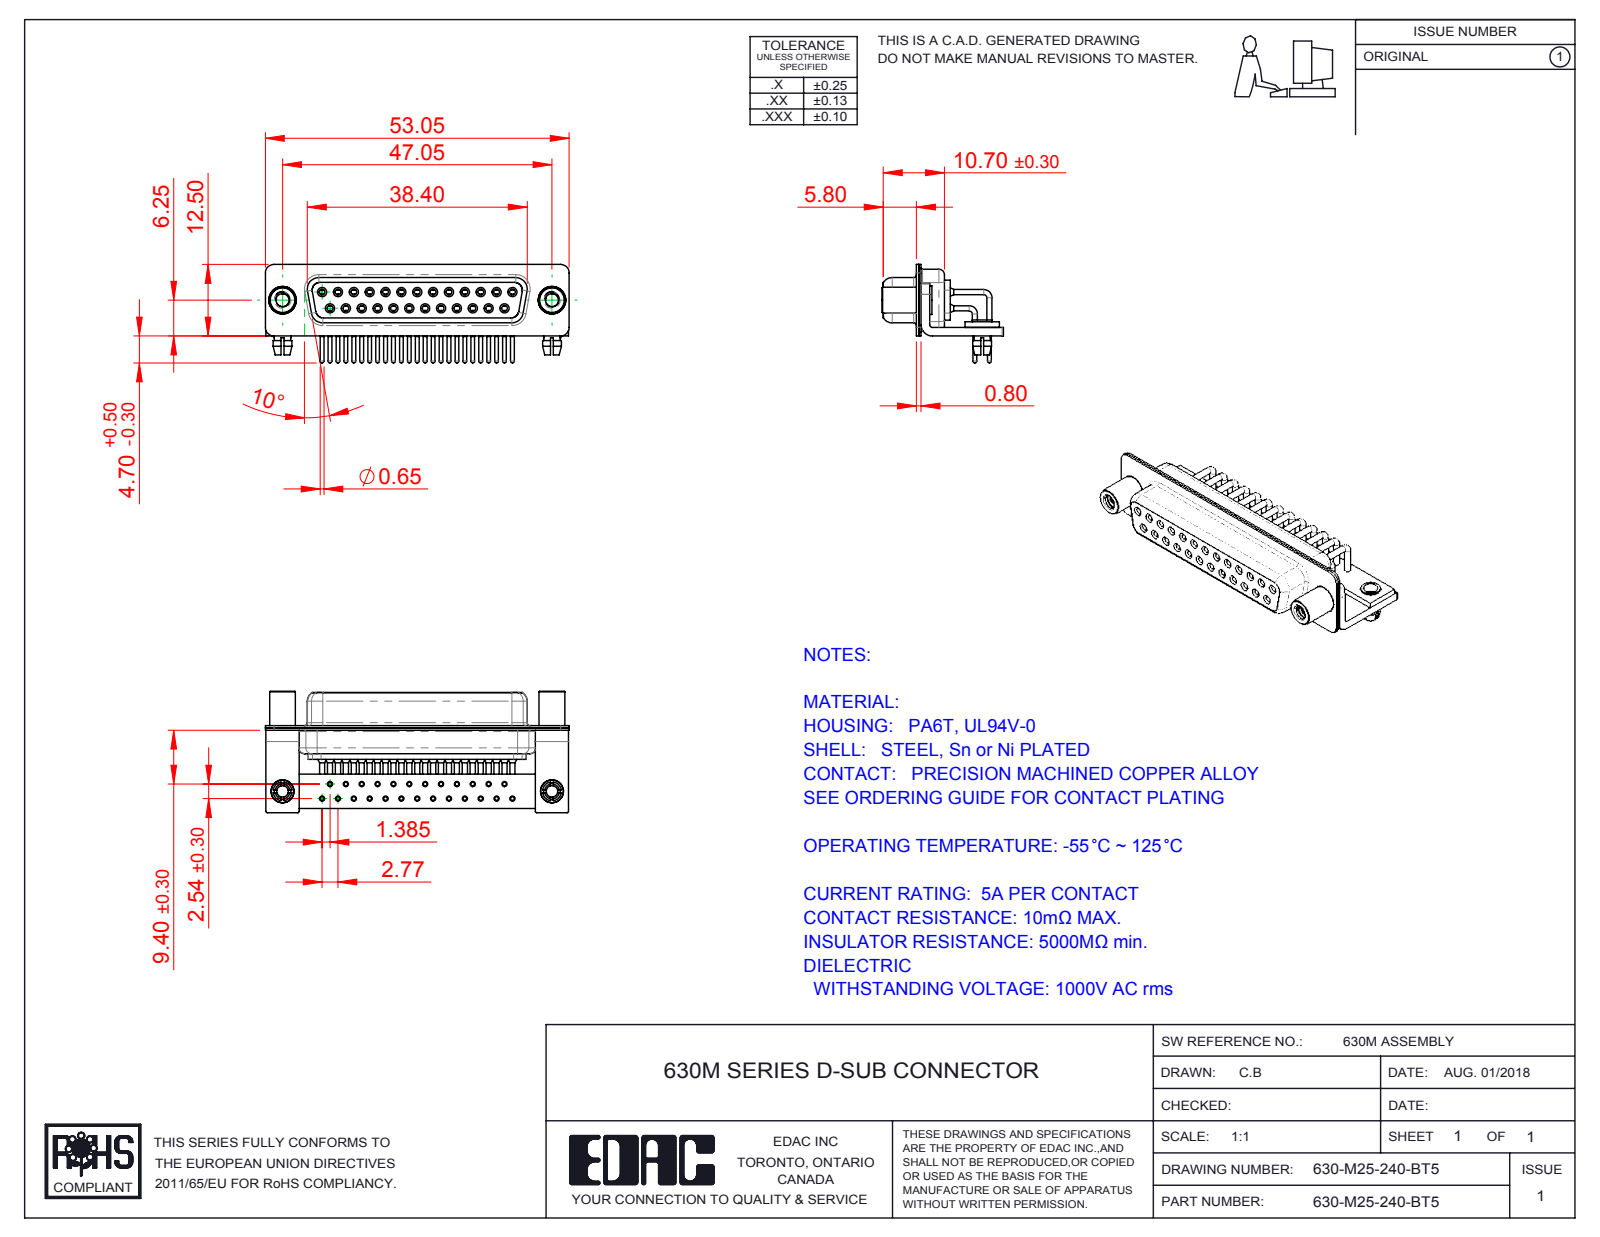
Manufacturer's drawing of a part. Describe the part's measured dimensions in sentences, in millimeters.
The part is named "630M Stabilizer Bracket; 630M Contact Row 1; 630-M25-240-BT5; 630M Shell Front_25 Contacts (+6 more)". Its 3-D file was written by "SolidWorks 2016 (CONFIG_CONTROL_DESIGN)". It is 35 solids with 1846 faces: 518 planar, 858 cylindrical and 470 other. Overall it measures 53.05 by 21.2 by 17.2 millimeters. Its volume is 4 624 cubic millimeters and its surface area 11 662 square millimeters. Round holes: 27 of diameter 2, 25 of diameter 0.9, 25 of diameter 1, 25 of diameter 1.1, 25 of diameter 1.7, 25 of diameter 1.8, 2 of diameter 2.26, 2 of diameter 2.5, 2 of diameter 3.2, 2 of diameter 4, 2 of diameter 4.8. Round bosses or shafts: 25 of diameter 1.6, 25 of diameter 1.5, 25 of diameter 0.9, 25 of diameter 0.65, 2 of diameter 5, 2 of diameter 4.9, 2 of diameter 4.5, 2 of diameter 4. Partial cylindrical surfaces (rounded edges, fillets, slot ends): 16 of radius 0.25, 16 of radius 1.5, 13 of radius 2, 10 of radius 1.35, 8 of radius 1.6, 5 of radius 0.5, 4 of radius 0.6, 4 of radius 0.65. The main face-to-face distances are 0.4, 2.3, 1.9, 9.35, 1.45, 8.95, 0.85, 0.8, 6.2, 1. The hole center spacings are 2.77, 5.54, 8.31, 11.08, 13.85, 3.16, 4.87, 16.62.
